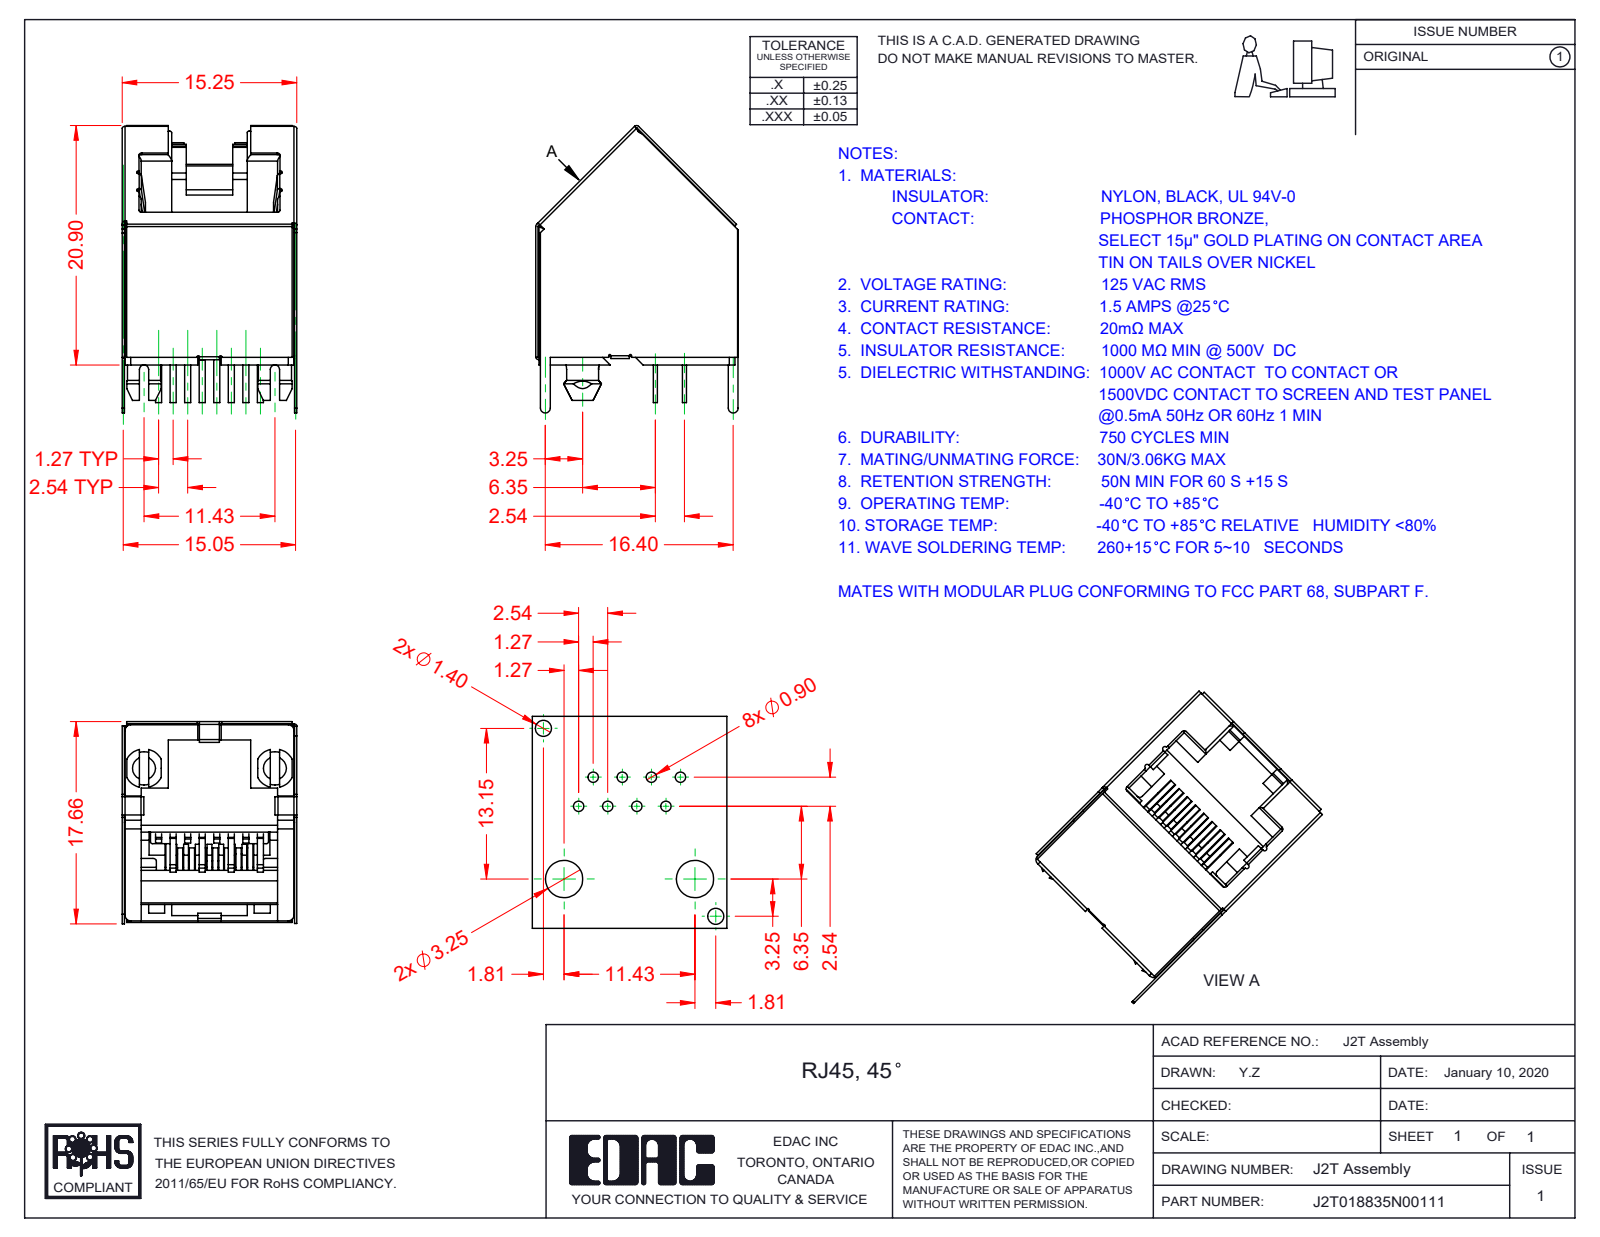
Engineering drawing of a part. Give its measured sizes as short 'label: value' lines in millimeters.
name: 2T Contacts; 2T Shell; 2T Contact Lock; RJ2T018835N00111 (+1 more)
written by: SolidWorks 2016 (CONFIG_CONTROL_DESIGN)
unit: mm
bodies: 11 solids, 631 faces (447 planar, 161 cylindrical, 23 other)
size: 25.09 × 17.66 × 15.25
volume: 1 960 mm³; area: 5 178 mm²
bosses: 2× ⌀2.9
rounds: 21× R0.5, 16× R1, 12× R0.2, 10× R0.25, 8× R1.46, 8× R1.52, 5× R0.1, 3× R0.3
face distances: 15.04, 1.42, 13.33, 14.8, 15, 15.24, 14.84, 14.99, 14.79, 14.75
